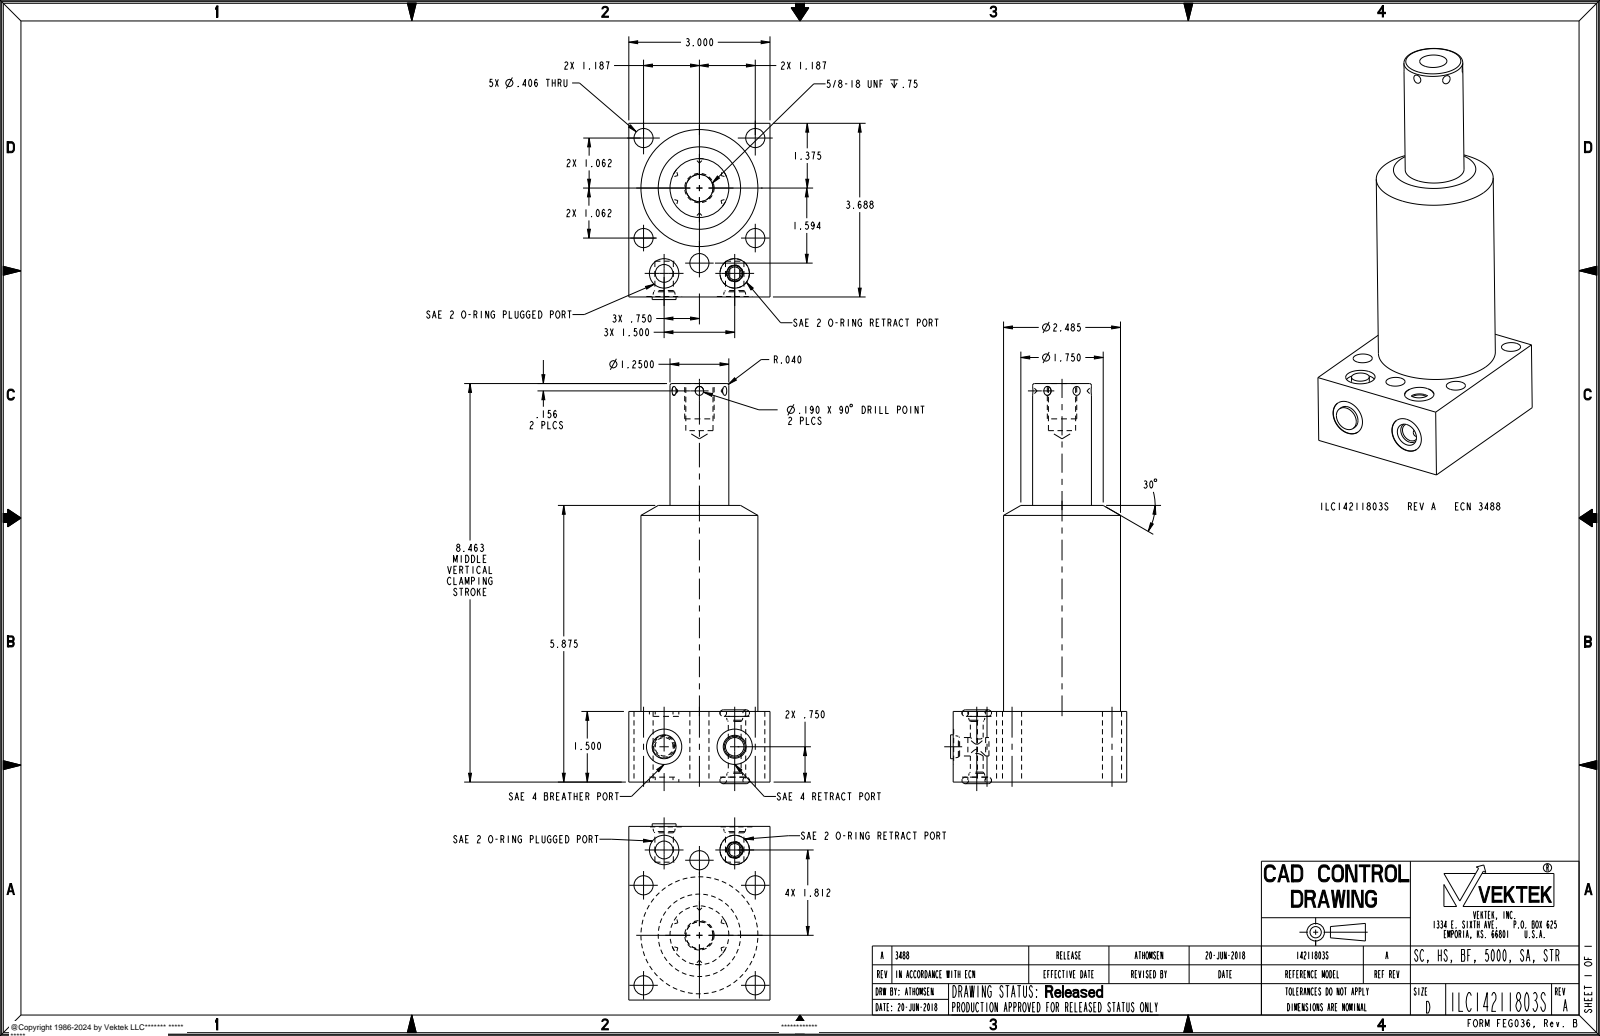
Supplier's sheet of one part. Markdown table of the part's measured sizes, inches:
| quantity | value |
| --- | --- |
| part name | ILC14211803S |
| STEP written by | PRO/ENGINEER BY PARAMETRIC TECHNOLOGY CORPORATION, 2013320 (AUTOMOTIVE_DESIGN) |
| units | inches |
| bodies | 3 solids, 111 faces (23 planar, 46 cylindrical, 42 other) |
| overall size | 8.497 × 3.743 × 3 |
| volume | 39.19 in³ |
| surface area | 102.2 in² |
| round holes (diameter × count) | 0.406 × 5, 0.392 × 2, 0.625 × 2, 0.75 × 2, 0.272 × 1, 0.578 × 1 |
| round bosses / shafts (diameter × count) | 2.485 × 1, 1.25 × 1, 0.625 × 1, 0.507 × 1, 0.378 × 1 |
| main face-to-face distances | 3, 1.5, 3.688, 5.875, 4.375, 8.463, 6.963, 2.588, 0.105, 1.395 |
| hole center spacings | 1.593, 0.781, 0.868, 1.301, 1.5, 1.961, 2.077, 2.124 |
